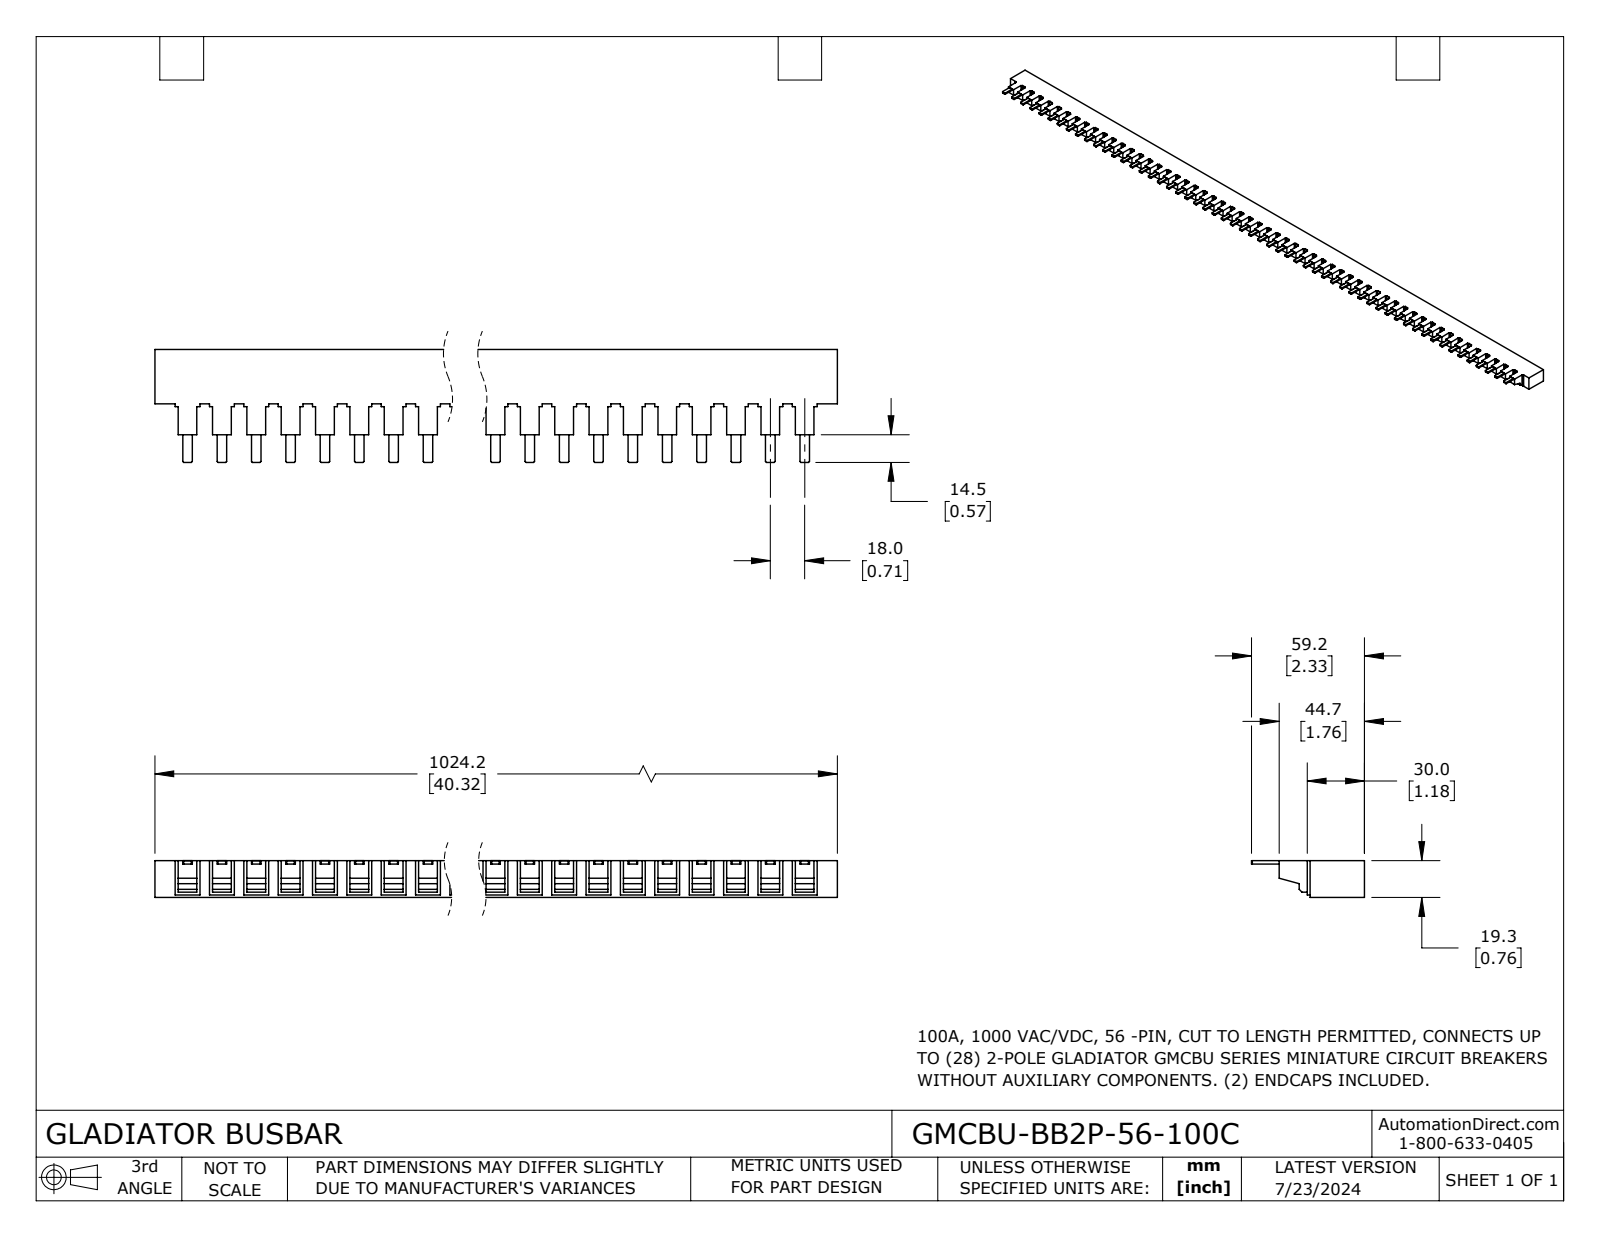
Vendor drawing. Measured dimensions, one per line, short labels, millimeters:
name: GMCBU-BB2P-56-100C
written by: SolidWorks 2023 (CONFIG_CONTROL_DESIGN)
unit: mm
bodies: 1 solid, 1014 faces (1014 planar, 0 cylindrical, 0 other)
size: 1024.2 × 59.2 × 19.3
volume: 689 100 mm³; area: 149 700 mm²
face distances: 19.3, 28.5, 1.5, 44.7, 16.2, 18, 30, 14.7, 1.8, 17.5
